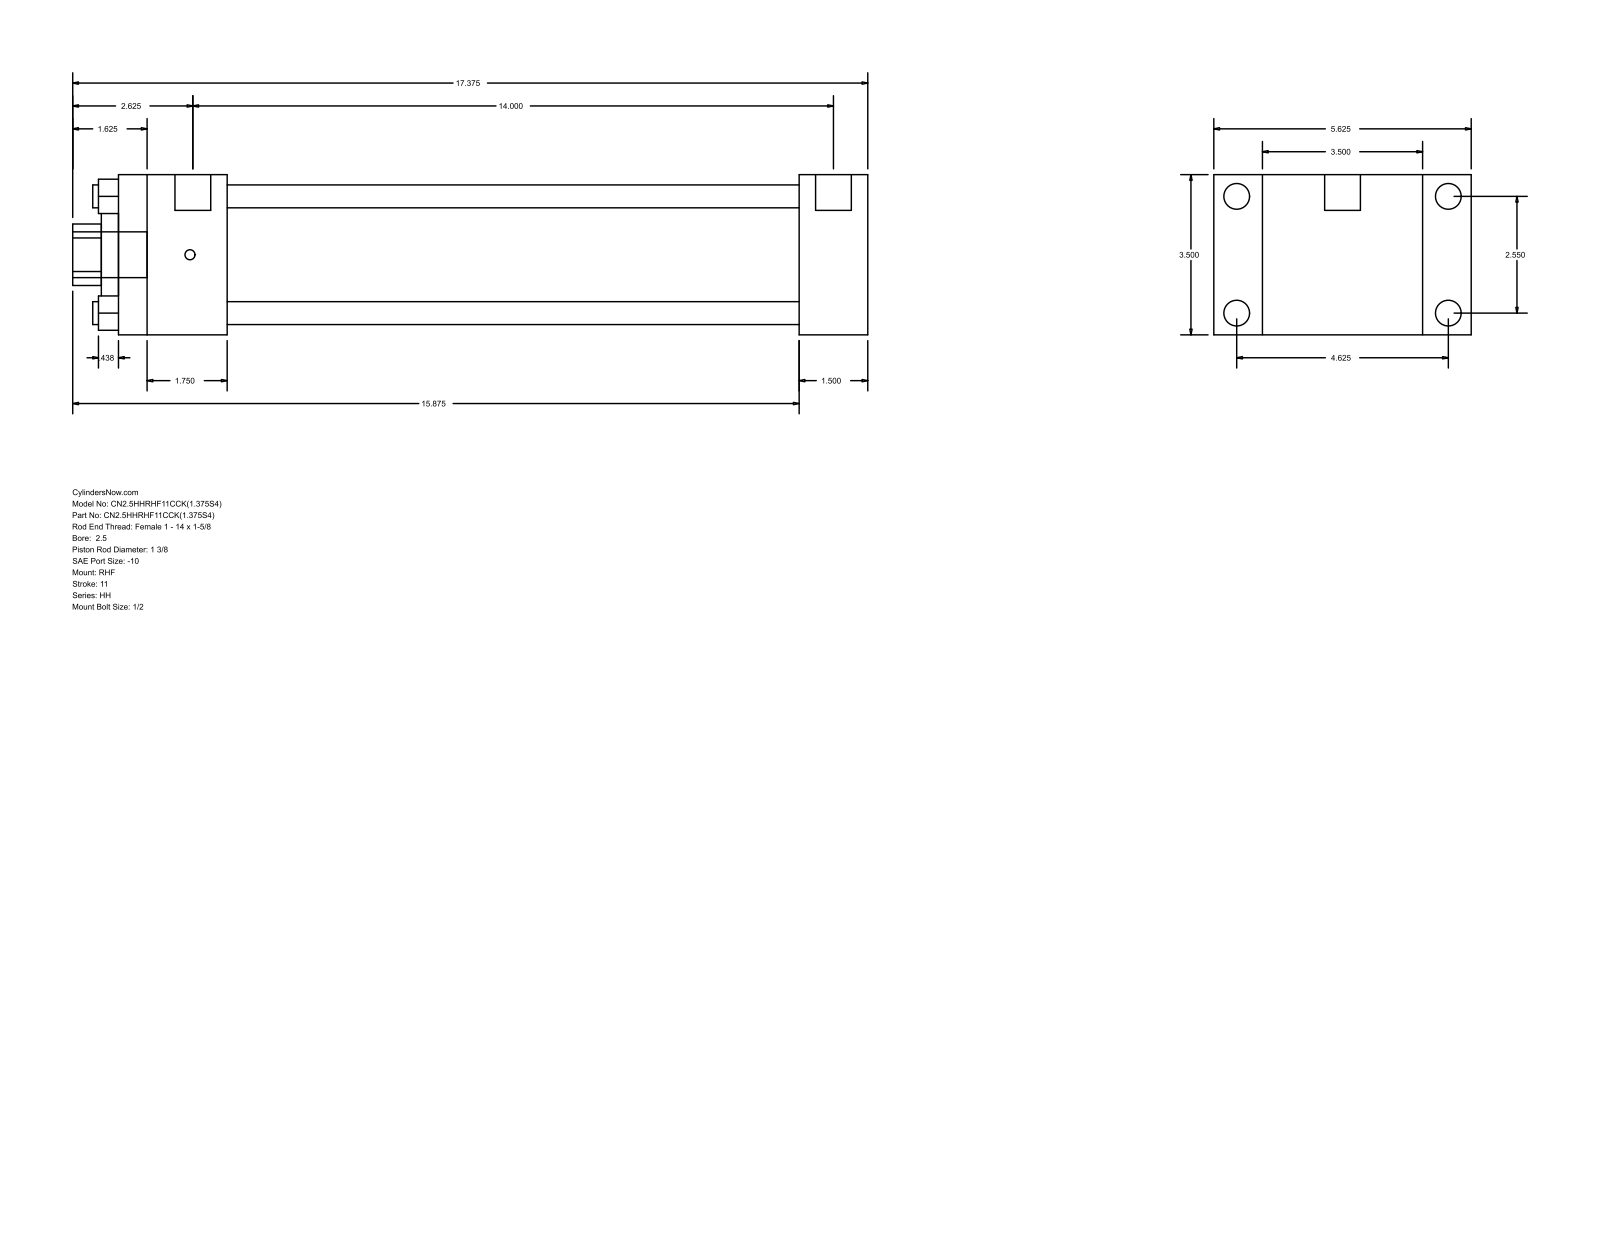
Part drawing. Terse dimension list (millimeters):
name: HH_RHF__0250_1.375
written by: GSSL Pune (CONFIG_CONTROL_DESIGN)
unit: mm
bodies: 0 solids, 88 faces (60 planar, 28 cylindrical, 0 other)
size: 441.32 × 142.88 × 88.9
holes: 4× ⌀12.7, 1× ⌀34.92, 1× ⌀50.8, 1× ⌀73.03
bosses: 4× ⌀14.3, 4× ⌀5.56, 2× ⌀19.84, 1× ⌀25.4
rounds: 1× R17.06
face distances: 88.9, 38.09, 26.99, 115.89, 377.83, 415.92, 142.88, 60.32, 317.51, 355.6
hole spacings: 45.79, 64.76, 91.58
